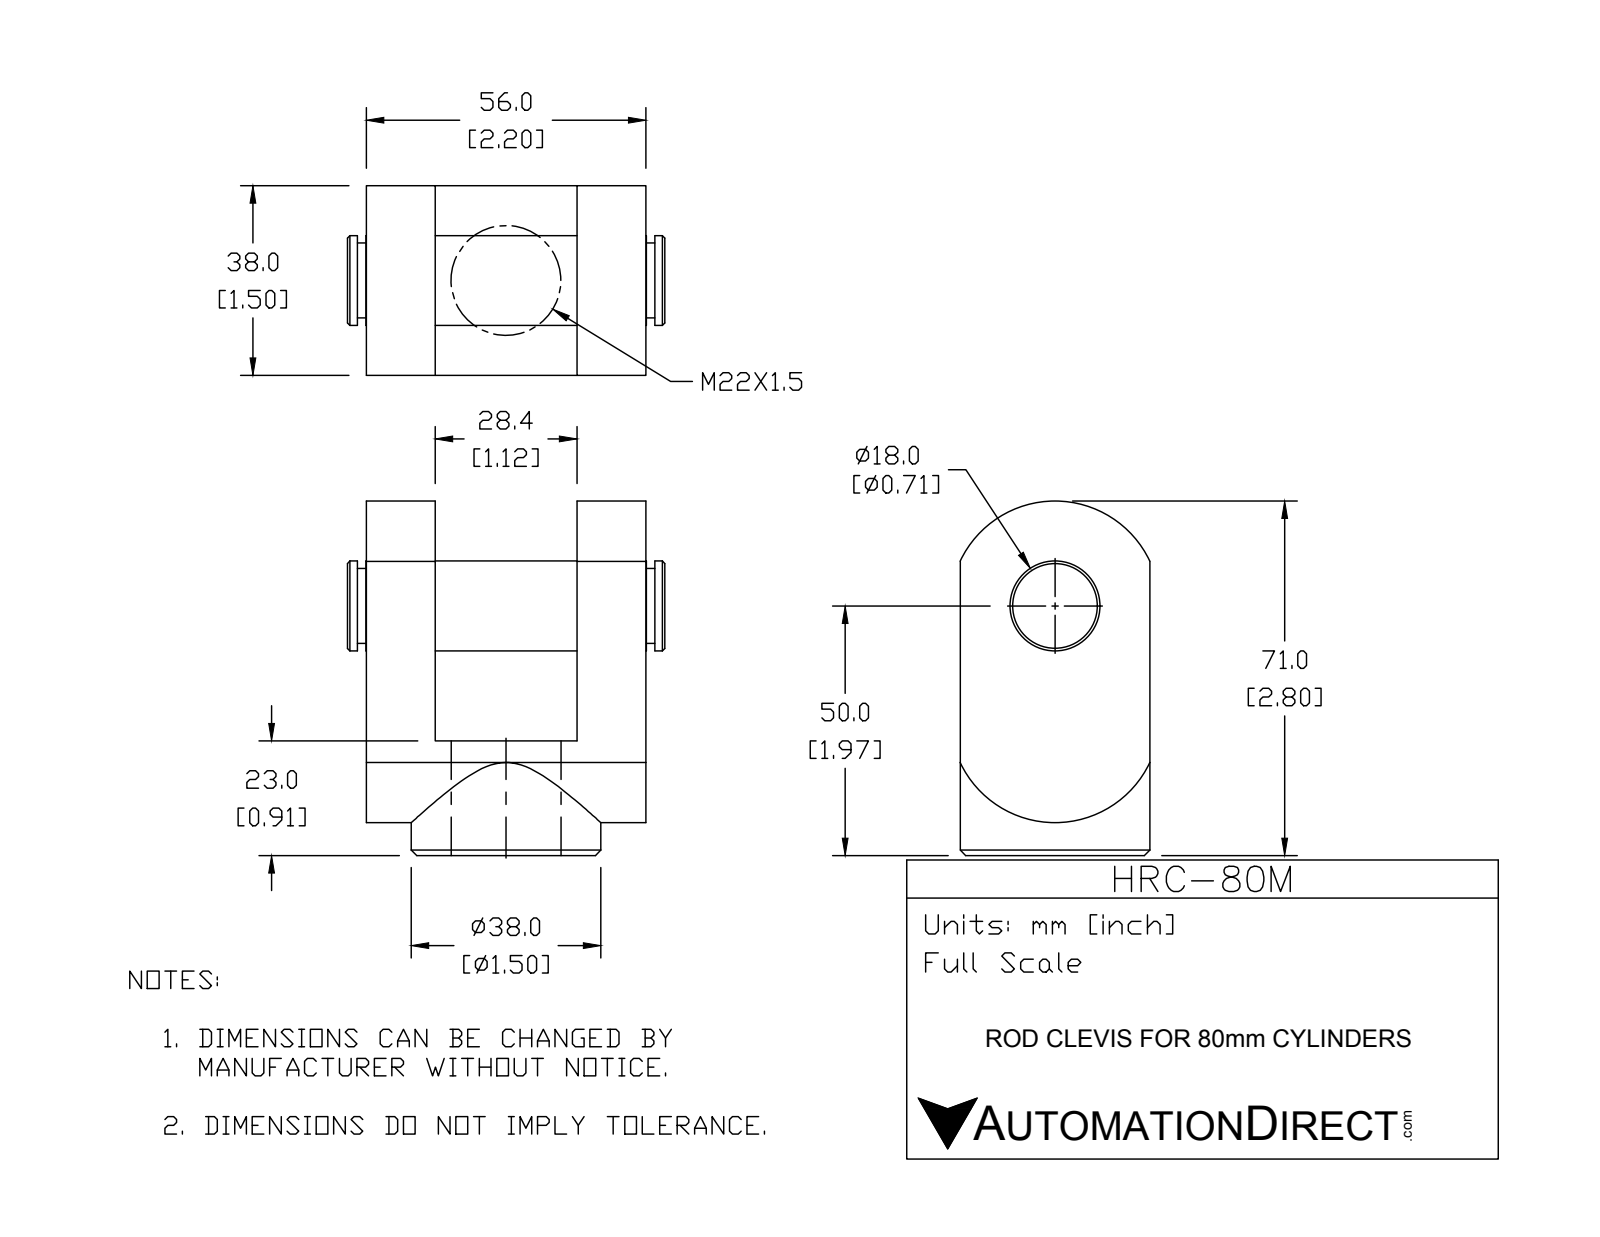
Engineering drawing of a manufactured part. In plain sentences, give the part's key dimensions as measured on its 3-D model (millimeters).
The part is named "HRC-80M". Its 3-D file was written by "SolidWorks 2015 (CONFIG_CONTROL_DESIGN)". It is 2 solids with 46 faces: 14 planar, 22 cylindrical and 10 other. Overall it measures 71 by 63.6 by 38 millimeters. Its volume is 85 886 cubic millimeters and its surface area 22 114 square millimeters. Round holes: 1 of diameter 20.5. Round bosses or shafts: 1 of diameter 38, 1 of diameter 18, 1 of diameter 15. Partial cylindrical surfaces (rounded edges, fillets, slot ends): 2 of radius 21. The main face-to-face distances are 13.8, 42.2, 56, 28.4, 38, 23, 3.8, 17.6, 46, 59.8.
